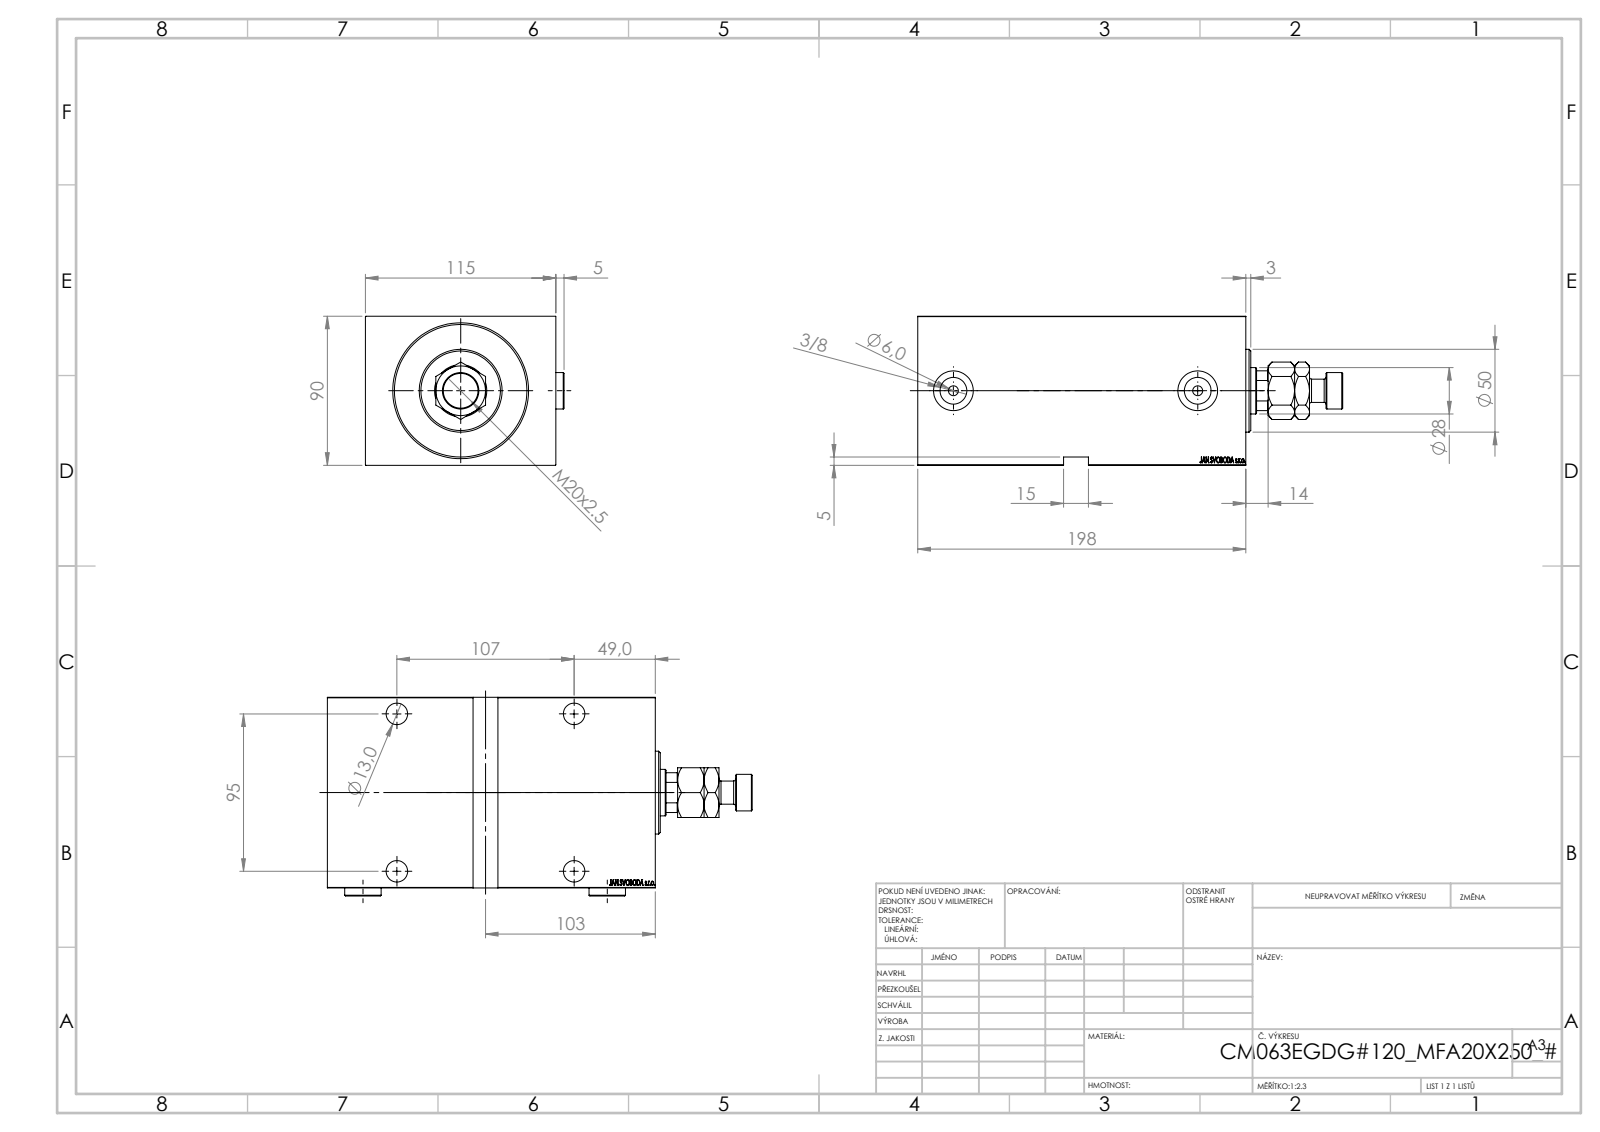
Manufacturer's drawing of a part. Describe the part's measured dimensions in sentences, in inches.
The part is named "Zatka_OIL_PORT; V450CM_E_VCP; V450CM_E_Body; MFA (+1 more)". Its 3-D file was written by "SolidWorks 2019 (CONFIG_CONTROL_DESIGN)". It is 6 solids with 964 faces: 462 planar, 72 cylindrical and 430 other. Overall it measures 10.098 by 4.72 by 3.543 inches. Its volume is 104.2 cubic inches and its surface area 325.3 square inches. Round holes: 4 of diameter 0.512, 4 of diameter 0.748, 2 of diameter 0.236, 2 of diameter 0.637, 2 of diameter 0.945, 1 of diameter 0.728, 1 of diameter 1.102, 1 of diameter 1.24, 1 of diameter 2.48, 1 of diameter 3.15. Round bosses or shafts: 3 of diameter 0.866, 1 of diameter 2.559, 1 of diameter 1.969, 1 of diameter 0.551. Partial cylindrical surfaces (rounded edges, fillets, slot ends): 1 of radius 0.531. The main face-to-face distances are 3.543, 4.528, 7.795, 0.689, 7.106, 0.197, 7.598, 6.909, 5.256, 7.142. The hole center spacings are 3.74, 4.213, 5.633, 5.807.
